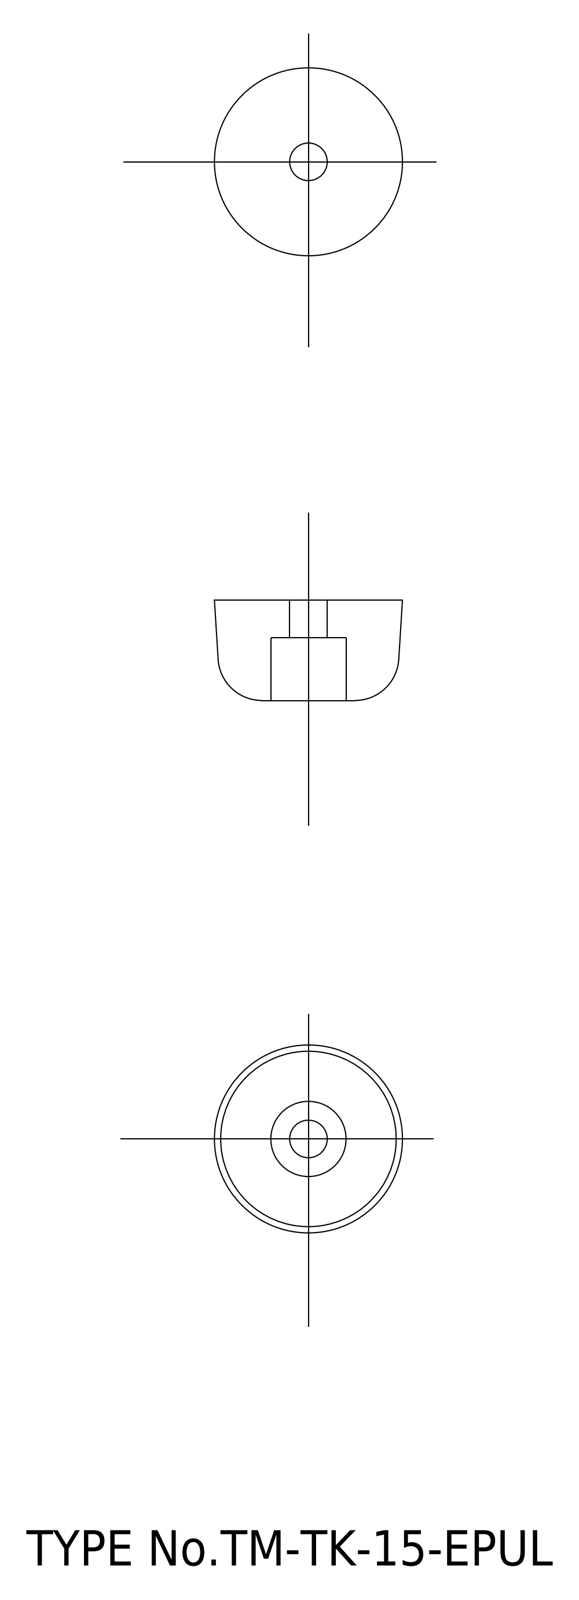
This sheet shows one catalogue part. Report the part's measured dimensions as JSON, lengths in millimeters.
{"part_name": "washer; rubber foot", "step_written_by": "spGate 15.6.1 (AUTOMOTIVE_DESIGN)", "units": "millimeters", "bodies": {"solids": 2, "faces": 23, "planar": 7, "cylindrical": 12, "other": 4}, "overall_size": [15, 15, 8], "volume_mm3": 1072, "surface_area_mm2": 960, "round_holes": [[3, 1], [3.5, 1], [6, 1], [9, 1]], "face_to_face_distances": [2.5, 0.5, 3, 5, 5.5, 8]}
